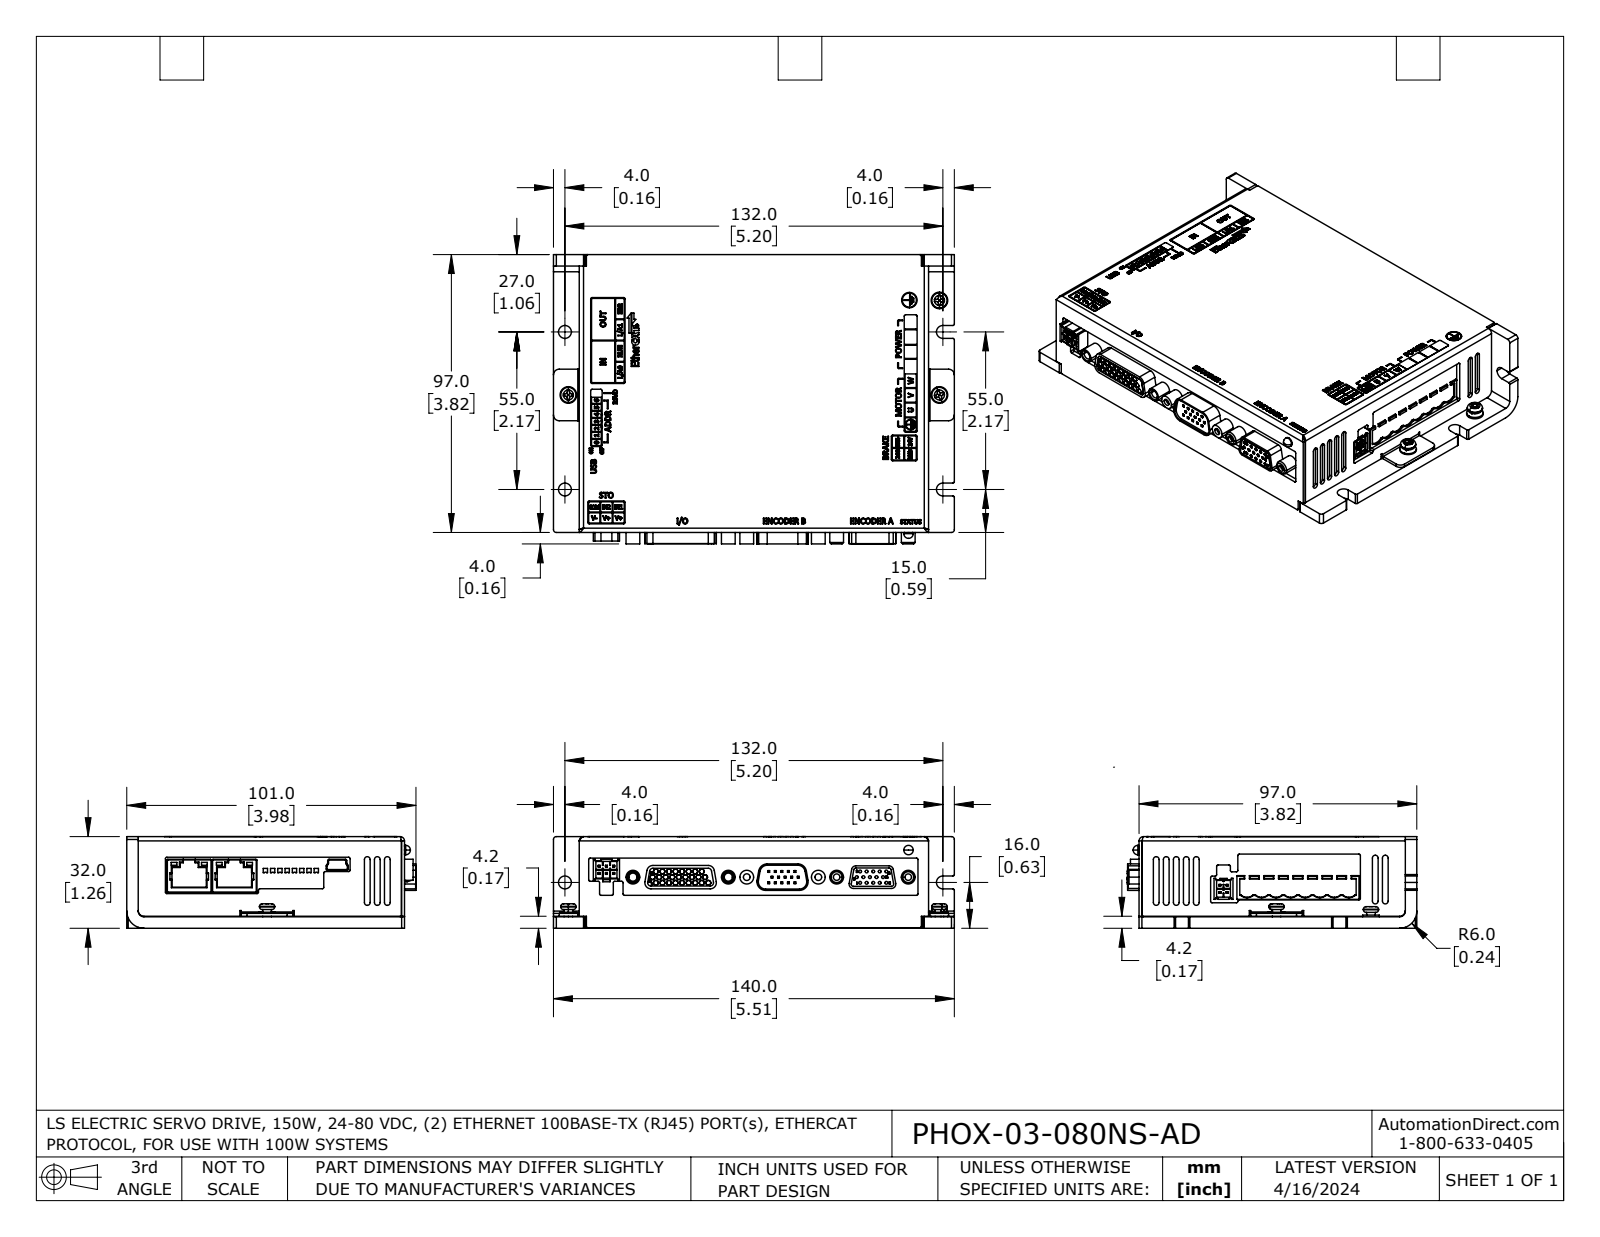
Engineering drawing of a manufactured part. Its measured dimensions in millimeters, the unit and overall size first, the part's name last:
Units: millimetres
Overall size (bounding box): 140 × 101 × 32
Round holes (diameter × count): ⌀1 ×15, ⌀2.5 ×3, ⌀4.5 ×3, ⌀2.3 ×2, ⌀2.4 ×2, ⌀2.8 ×2, ⌀3.7 ×2, ⌀0.9 ×1, ⌀3.3 ×1, ⌀4.9 ×1
Round bosses / shafts (diameter × count): ⌀4.8 ×6, ⌀5.8 ×3, ⌀5.3 ×3, ⌀3 ×3, ⌀5.4 ×1, ⌀3.7 ×1, ⌀3.3 ×1, ⌀1.1 ×1
Partial cylindrical surfaces — rounded edges, fillets, slot ends (radius × count): R0.5 ×91, R0.2 ×22, R1 ×18, R0.9 ×12, R0.3 ×9, R1.5 ×9, R0.8 ×8, R2 ×6
Main face-to-face distances: 32, 4, 97, 1.5, 28, 122, 120.5, 1, 9, 10.5
Hole centre spacings: 2.3, 6, 4, 2.3, 4.6, 8.3, 4.6, 4
Volume: 385 800 mm³ · Surface area: 47 510 mm²
Bodies: 4 solids, 3941 faces (2416 planar, 365 cylindrical, 1160 other)
Part name (STEP PRODUCT): PHOX-03-080NS-AD
STEP written by: SolidWorks 2021 (AUTOMOTIVE_DESIGN)
